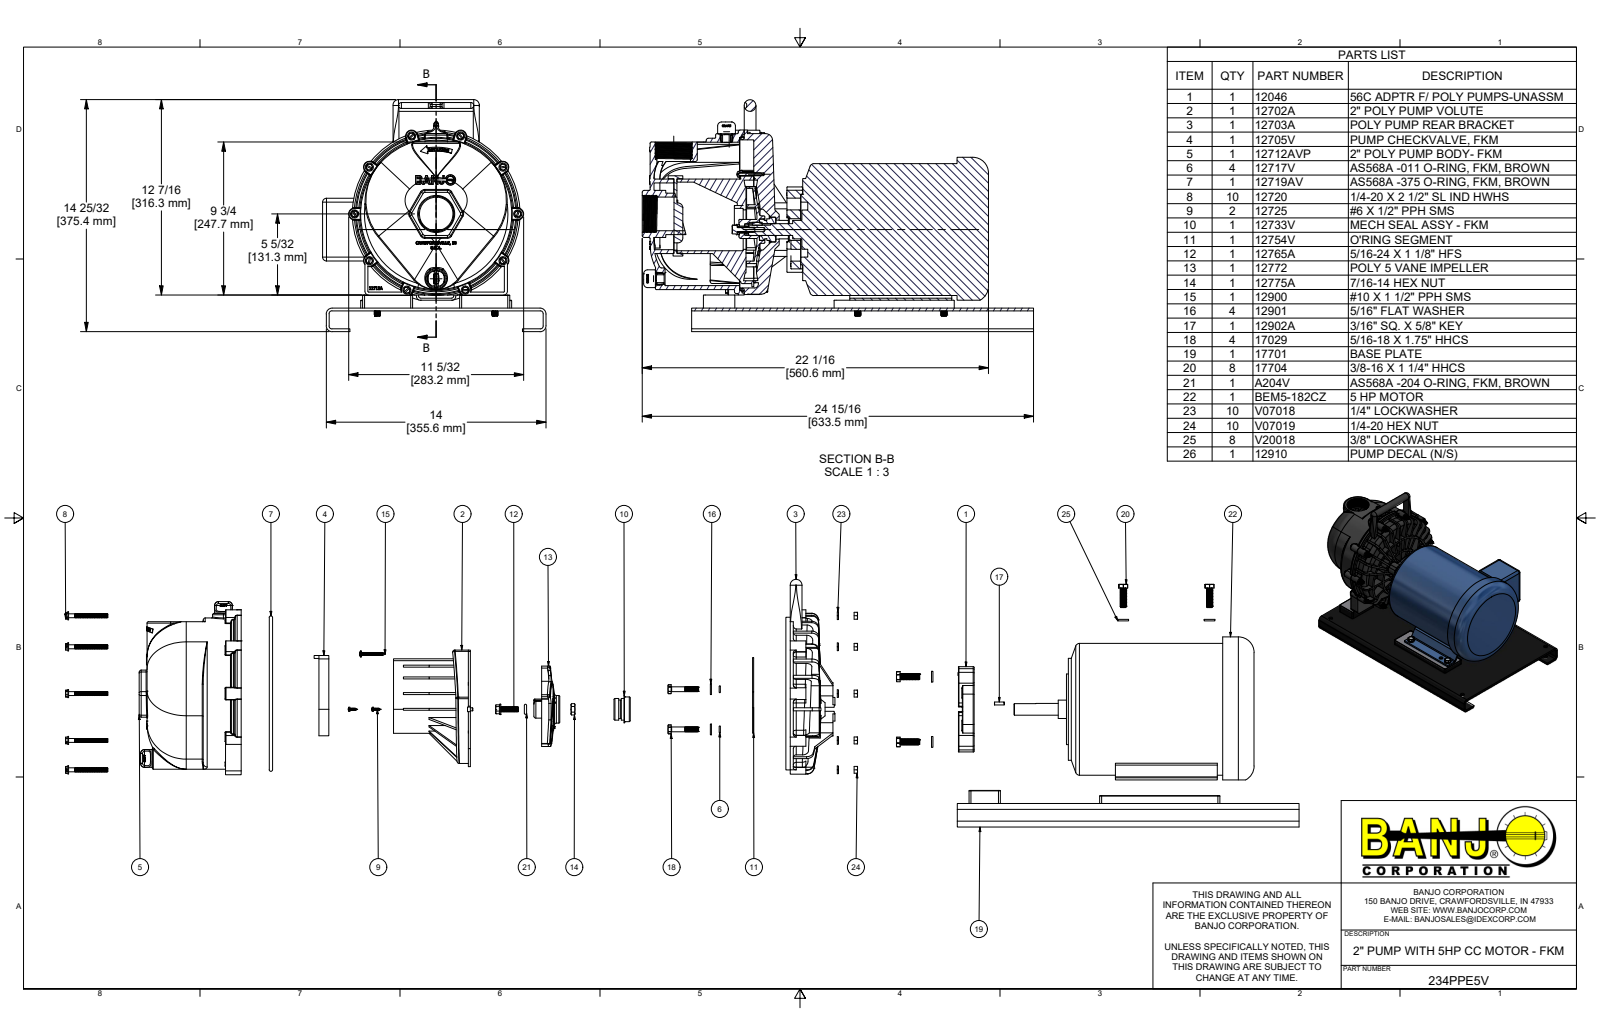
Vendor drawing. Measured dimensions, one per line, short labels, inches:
name: 234PPE5V; 12703A; 12046; 12046X (+8 more)
written by: Autodesk Inventor 2019 (AUTOMOTIVE_DESIGN)
unit: in
bodies: 107 solids, 11146 faces (3002 planar, 3221 cylindrical, 4923 other)
size: 24.94 × 14.781 × 14.24
volume: 1 006 in³; area: 3 335 in²
holes: 16× ⌀0.307, 14× ⌀0.252, 10× ⌀0.196, 10× ⌀0.27, 10× ⌀0.41, 8× ⌀0.385, 7× ⌀0.22, 6× ⌀0.5, 4× ⌀0.344, 4× ⌀0.359, 4× ⌀0.401, 4× ⌀0.406
bosses: 152× ⌀0.324, 60× ⌀0.268, 10× ⌀0.52, 10× ⌀0.489, 10× ⌀0.25, 8× ⌀0.687, 8× ⌀0.375, 6× ⌀0.192
rounds: 166× R0.03, 65× R0.25, 47× R0.125, 29× R0.5, 27× R0.06, 26× R0.008, 24× R0.187, 16× R0.162
face distances: 0.18, 0.5, 2, 0.179, 0.68, 1.5, 1.321, 1.32, 1.141, 1.821
hole spacings: 2.561, 3.452, 5.2, 1, 1.125, 1.128, 2.615, 2.937
